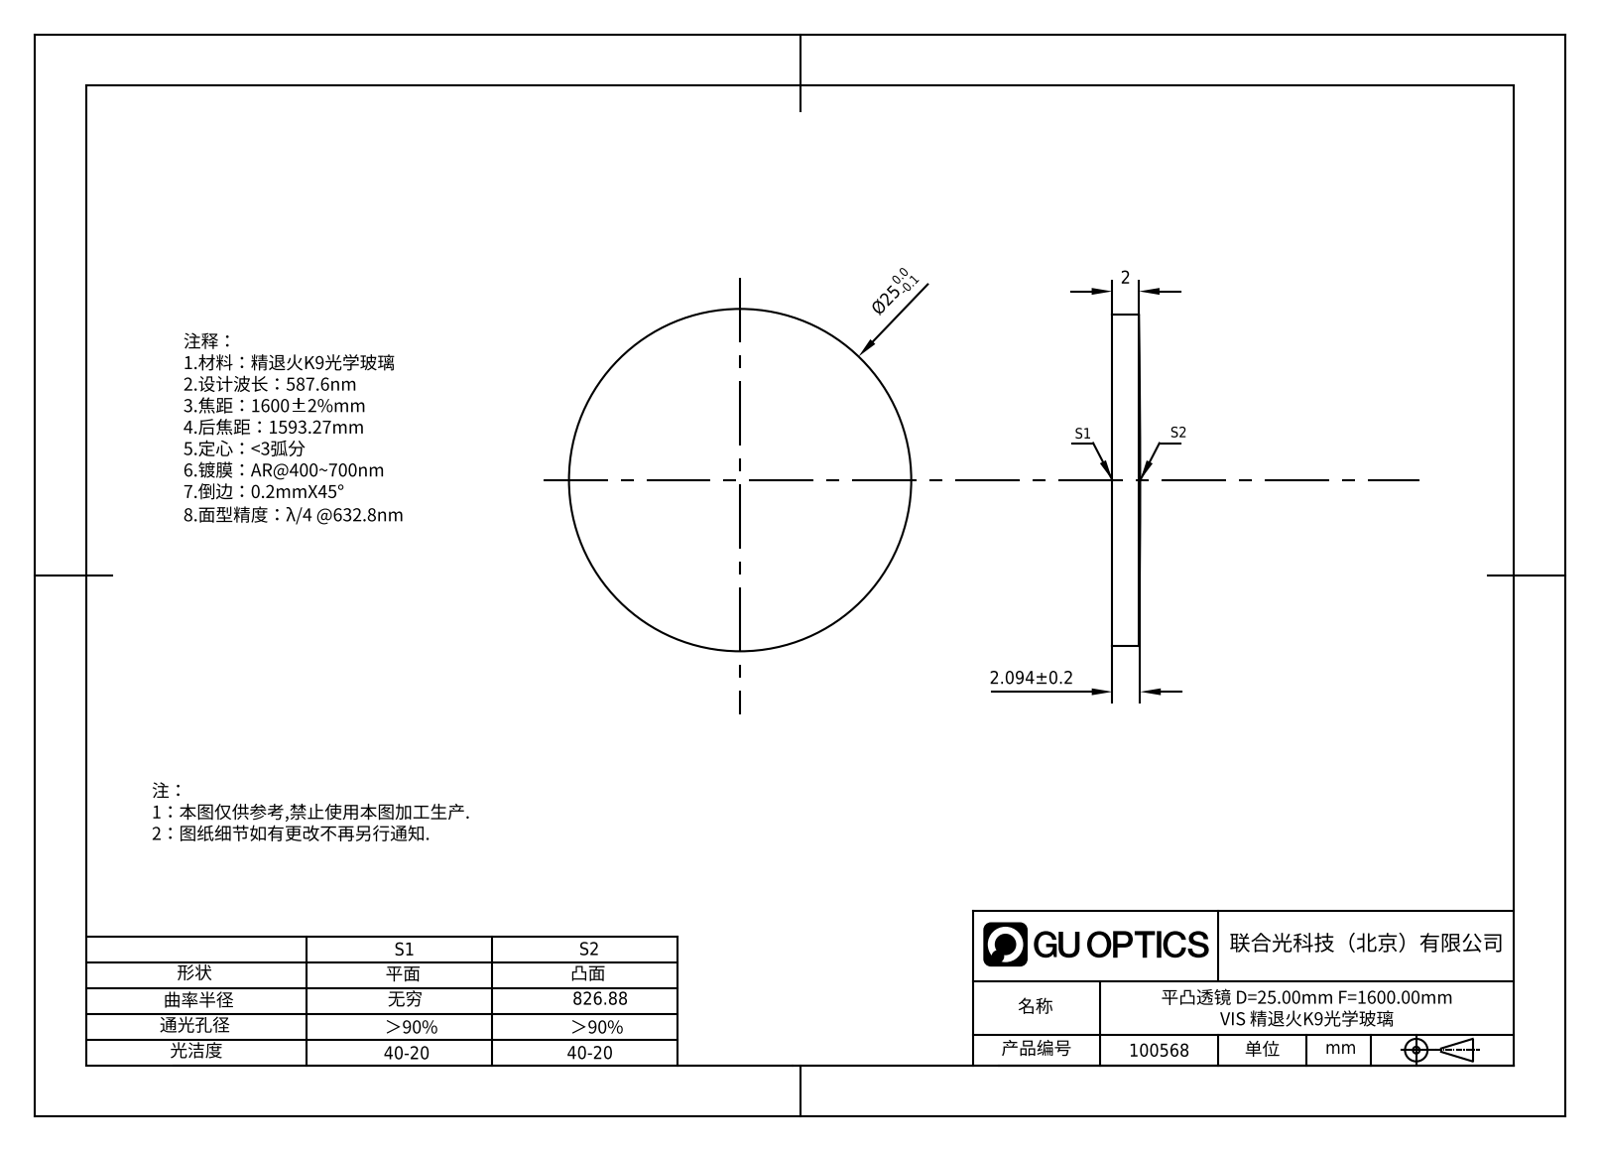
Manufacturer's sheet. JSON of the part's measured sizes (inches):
{"part_name": "100568", "step_written_by": "SolidWorks 2020 (CONFIG_CONTROL_DESIGN)", "units": "inches", "bodies": {"solids": 1, "faces": 5, "planar": 1, "cylindrical": 2, "other": 2}, "overall_size": [0.984, 0.984, 0.095], "volume_in3": 0.068, "surface_area_in2": 1.767, "round_bosses_or_shafts": [[0.984, 1]]}
